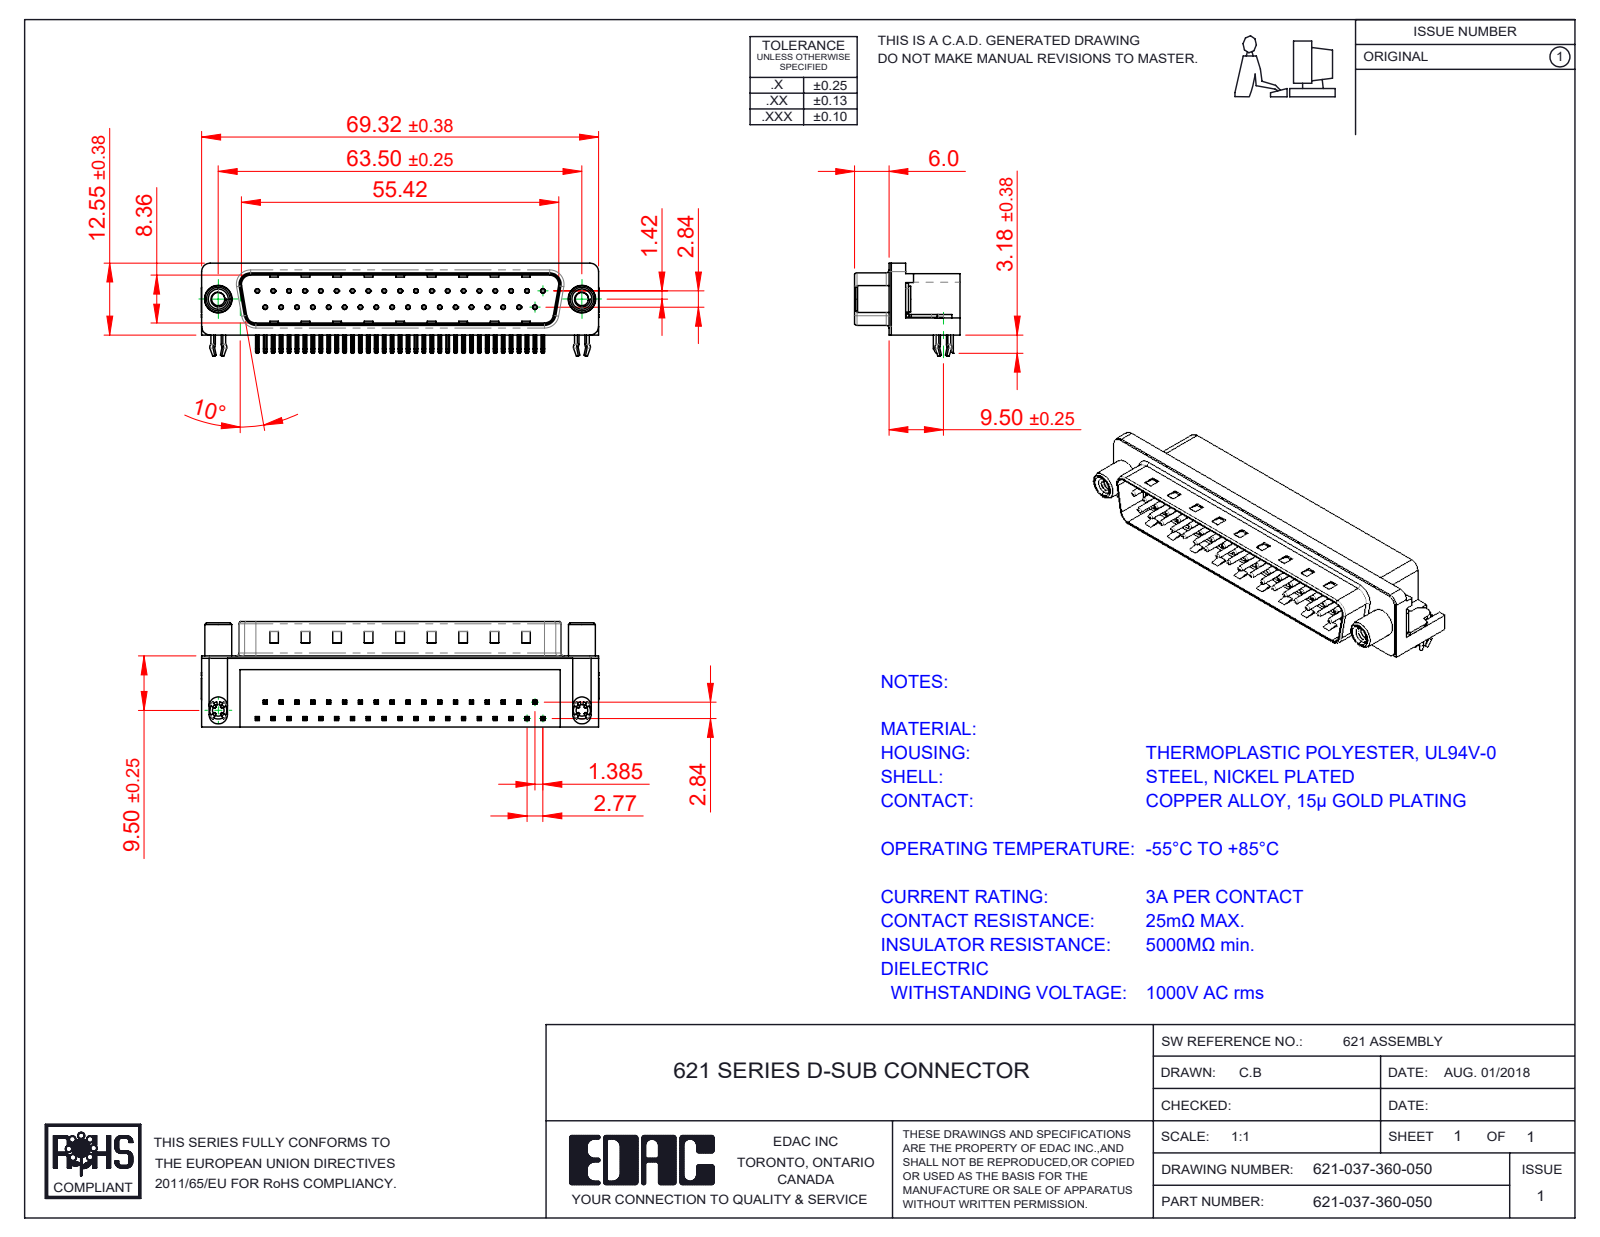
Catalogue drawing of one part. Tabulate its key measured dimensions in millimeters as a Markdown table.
| quantity | value |
| --- | --- |
| part name | 621 Shell_37 Socket; 621 Round Threaded Standoff; 621 Housing_37 Socket; 621 Contact Bottom (+3 more) |
| STEP written by | SolidWorks 2016 (CONFIG_CONTROL_DESIGN) |
| units | millimeters |
| bodies | 43 solids, 3223 faces (2005 planar, 935 cylindrical, 283 other) |
| overall size | 69.4 × 18.4 × 15.73 |
| volume | 8 723 mm³ |
| surface area | 10 373 mm² |
| round holes (diameter × count) | 0.35 × 37, 0.8 × 37, 2.26 × 2, 2.3 × 2, 3.1 × 2, 4 × 2, 4.8 × 2, 5 × 2 |
| round bosses / shafts (diameter × count) | 0.75 × 37, 4.9 × 2, 4.7 × 2, 4.5 × 2, 3.85 × 2, 3.26 × 2 |
| partial cylindrical surfaces (radius × count) | 0.25 × 148, 0.12 × 74, 1 × 16, 0.5 × 9, 1.6 × 8, 1.5 × 7, 0.9 × 4, 2 × 4 |
| main face-to-face distances | 0.4, 12, 10.35, 8.76, 2.1, 1.7, 10.46, 10.86, 9, 12.4 |
| hole center spacings | 3.16, 2.77, 5.54, 8.31, 11.08, 13.85, 19.39, 22.16 |
